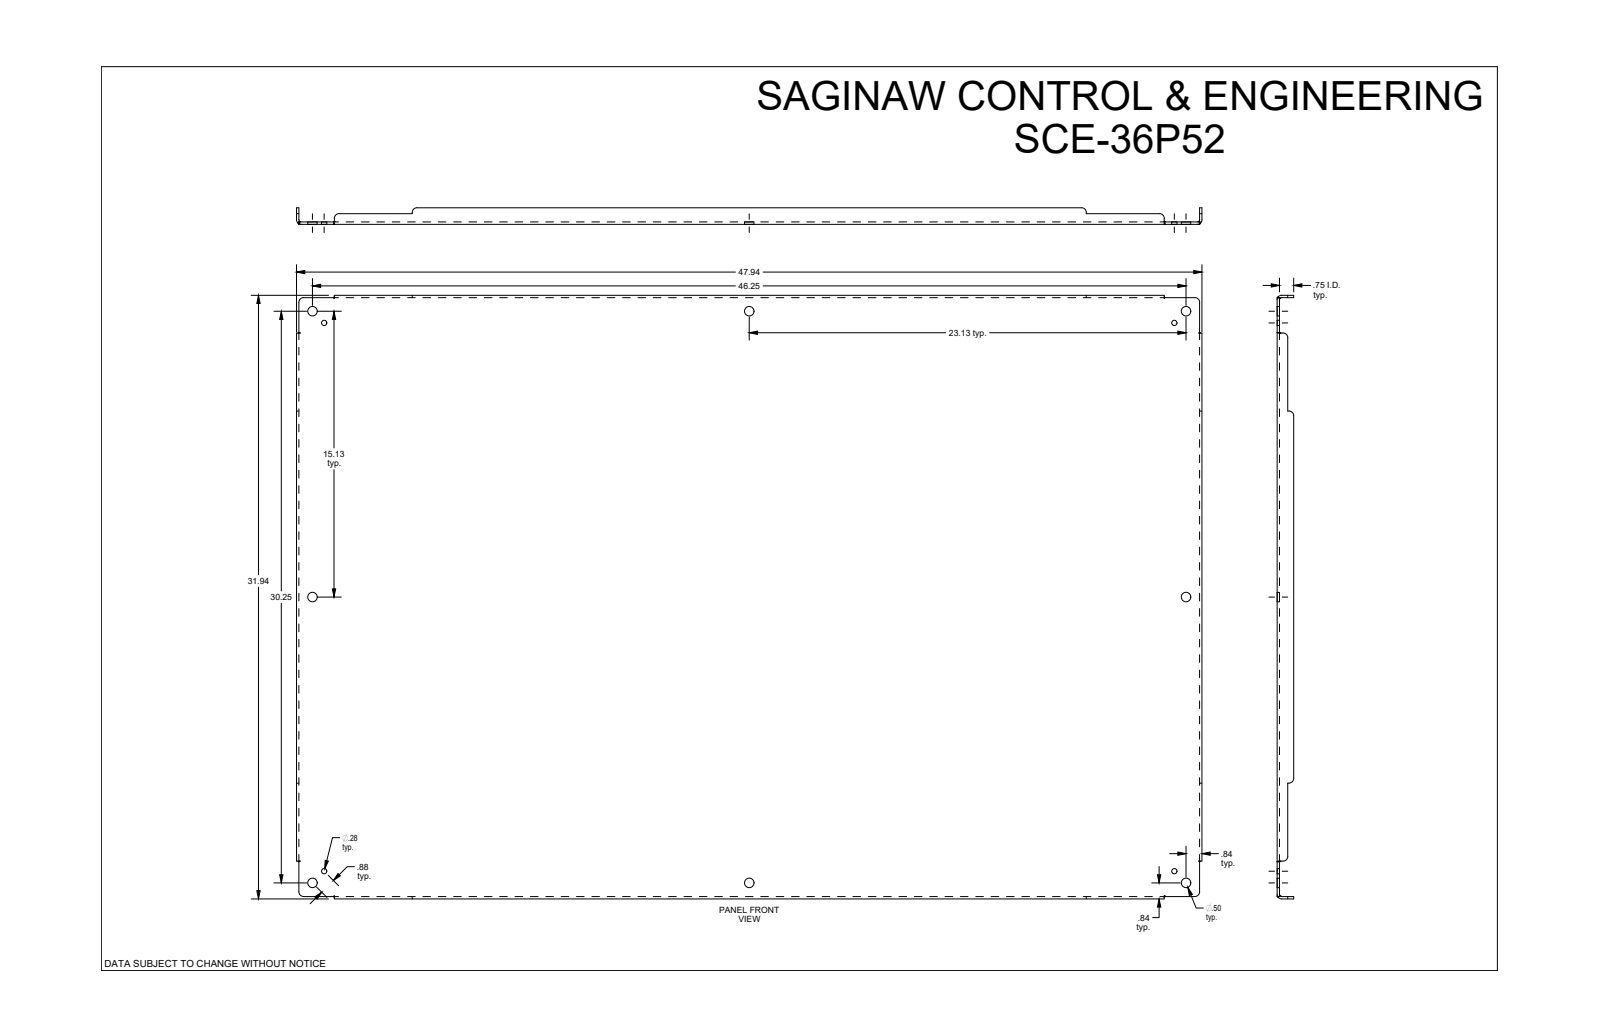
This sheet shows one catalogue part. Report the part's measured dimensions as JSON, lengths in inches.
{"part_name": "SCE-36P52", "step_written_by": "SolidWorks 2019 (AUTOMOTIVE_DESIGN)", "units": "inches", "bodies": {"solids": 1, "faces": 110, "planar": 46, "cylindrical": 40, "other": 24}, "overall_size": [47.938, 31.938, 0.875], "volume_in3": 201.7, "surface_area_in2": 3250, "round_holes": [[0.5, 8], [0.281, 4]], "partial_cylinders_radius": [[0.25, 12], [0.112, 4], [0.237, 4]], "face_to_face_distances": [0.125, 0.125, 31.813, 47.813, 31.687, 31.938, 47.687, 47.938, 0.75, 0.875], "hole_center_spacings": [0.875, 14.52, 15.125, 22.515, 23.125, 27.632, 29.637, 37.209]}
